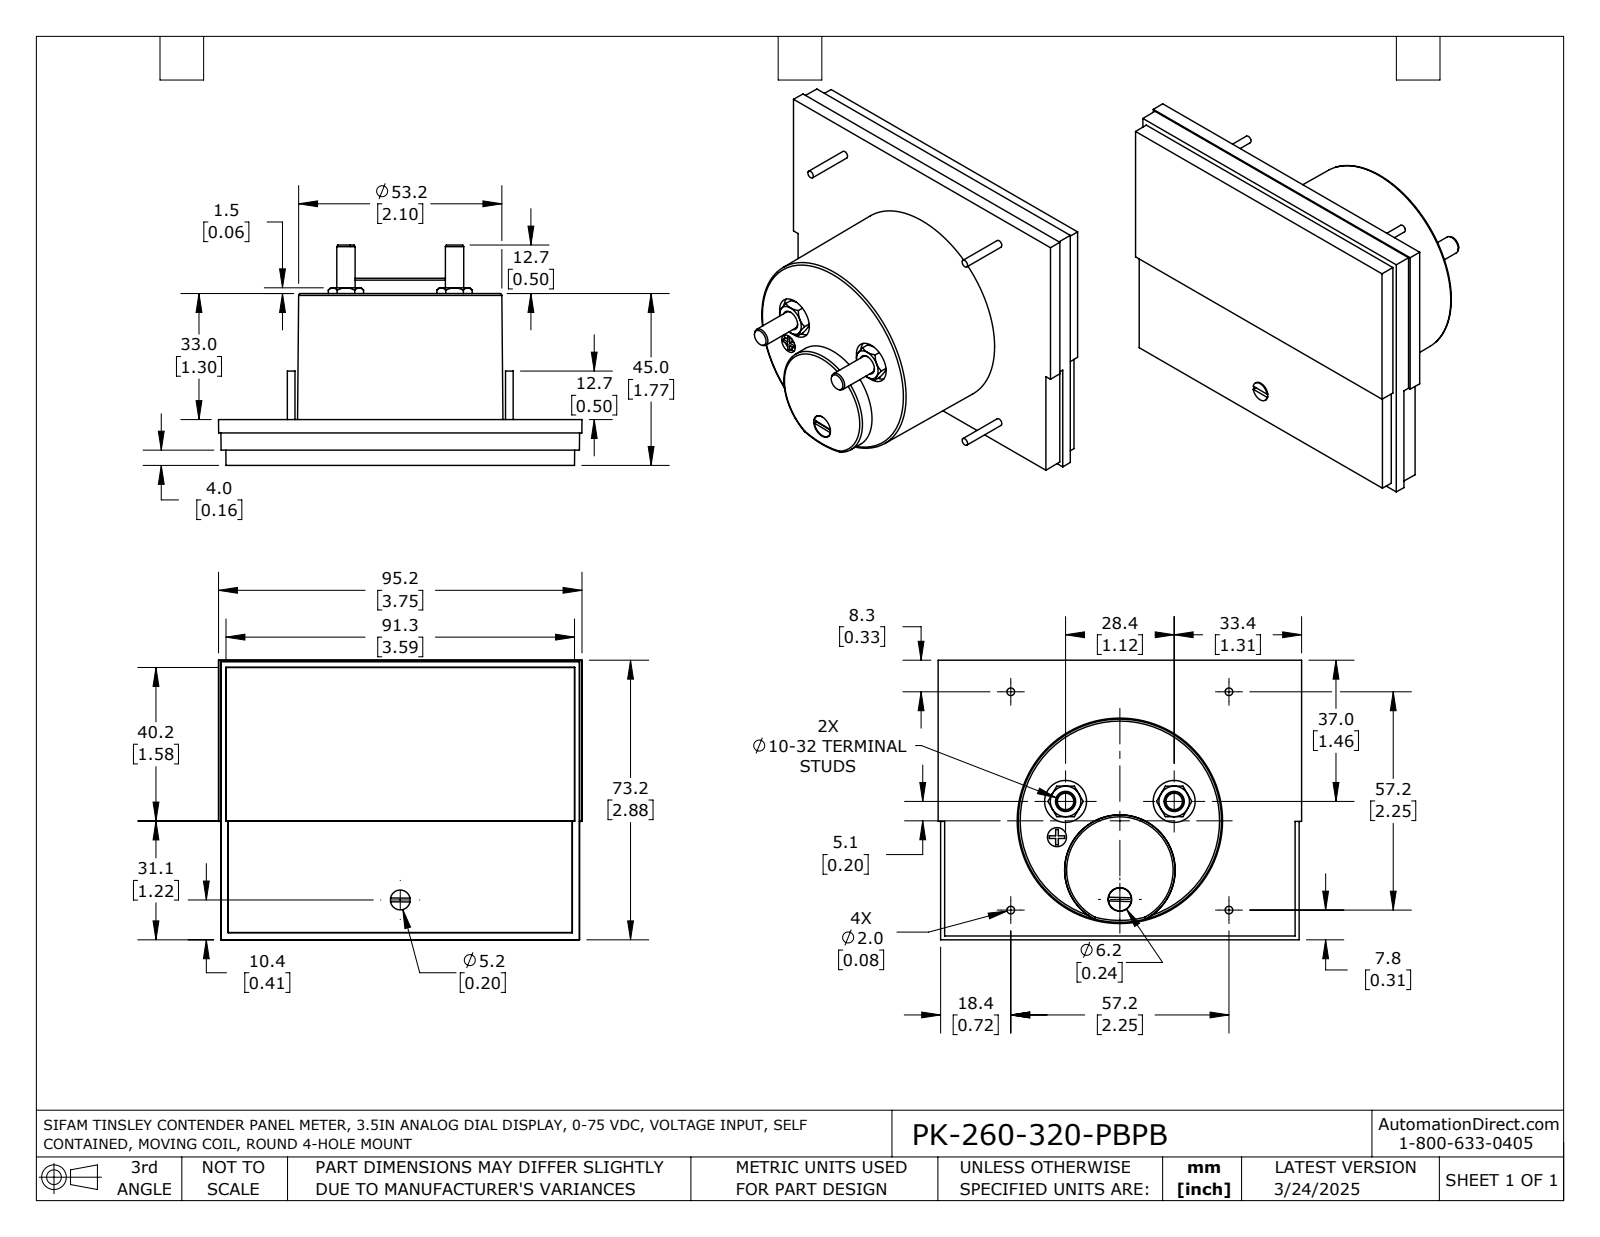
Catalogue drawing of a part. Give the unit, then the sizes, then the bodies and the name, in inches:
Units: inches
Overall size (bounding box): 3.748 × 2.882 × 2.272
Round holes (diameter × count): ⌀0.433 ×2, ⌀0.197 ×1, ⌀0.244 ×1
Round bosses / shafts (diameter × count): ⌀0.079 ×4, ⌀0.189 ×2, ⌀0.236 ×1, ⌀0.205 ×1
Partial cylindrical surfaces — rounded edges, fillets, slot ends (radius × count): R0.1 ×1
Main face-to-face distances: 0.472, 0.03, 0.443, 1.772, 1.299, 1.742, 0.157, 0.073, 0.315, 1.457
Hole centre spacings: 1.155, 0.379, 0.912, 1.12, 1.263
Volume: 9.446 in³ · Surface area: 38.39 in²
Bodies: 1 solid, 163 faces (76 planar, 31 cylindrical, 56 other)
Part name (STEP PRODUCT): PK-260-320-PBPB
STEP written by: SolidWorks 2021 (AUTOMOTIVE_DESIGN)
